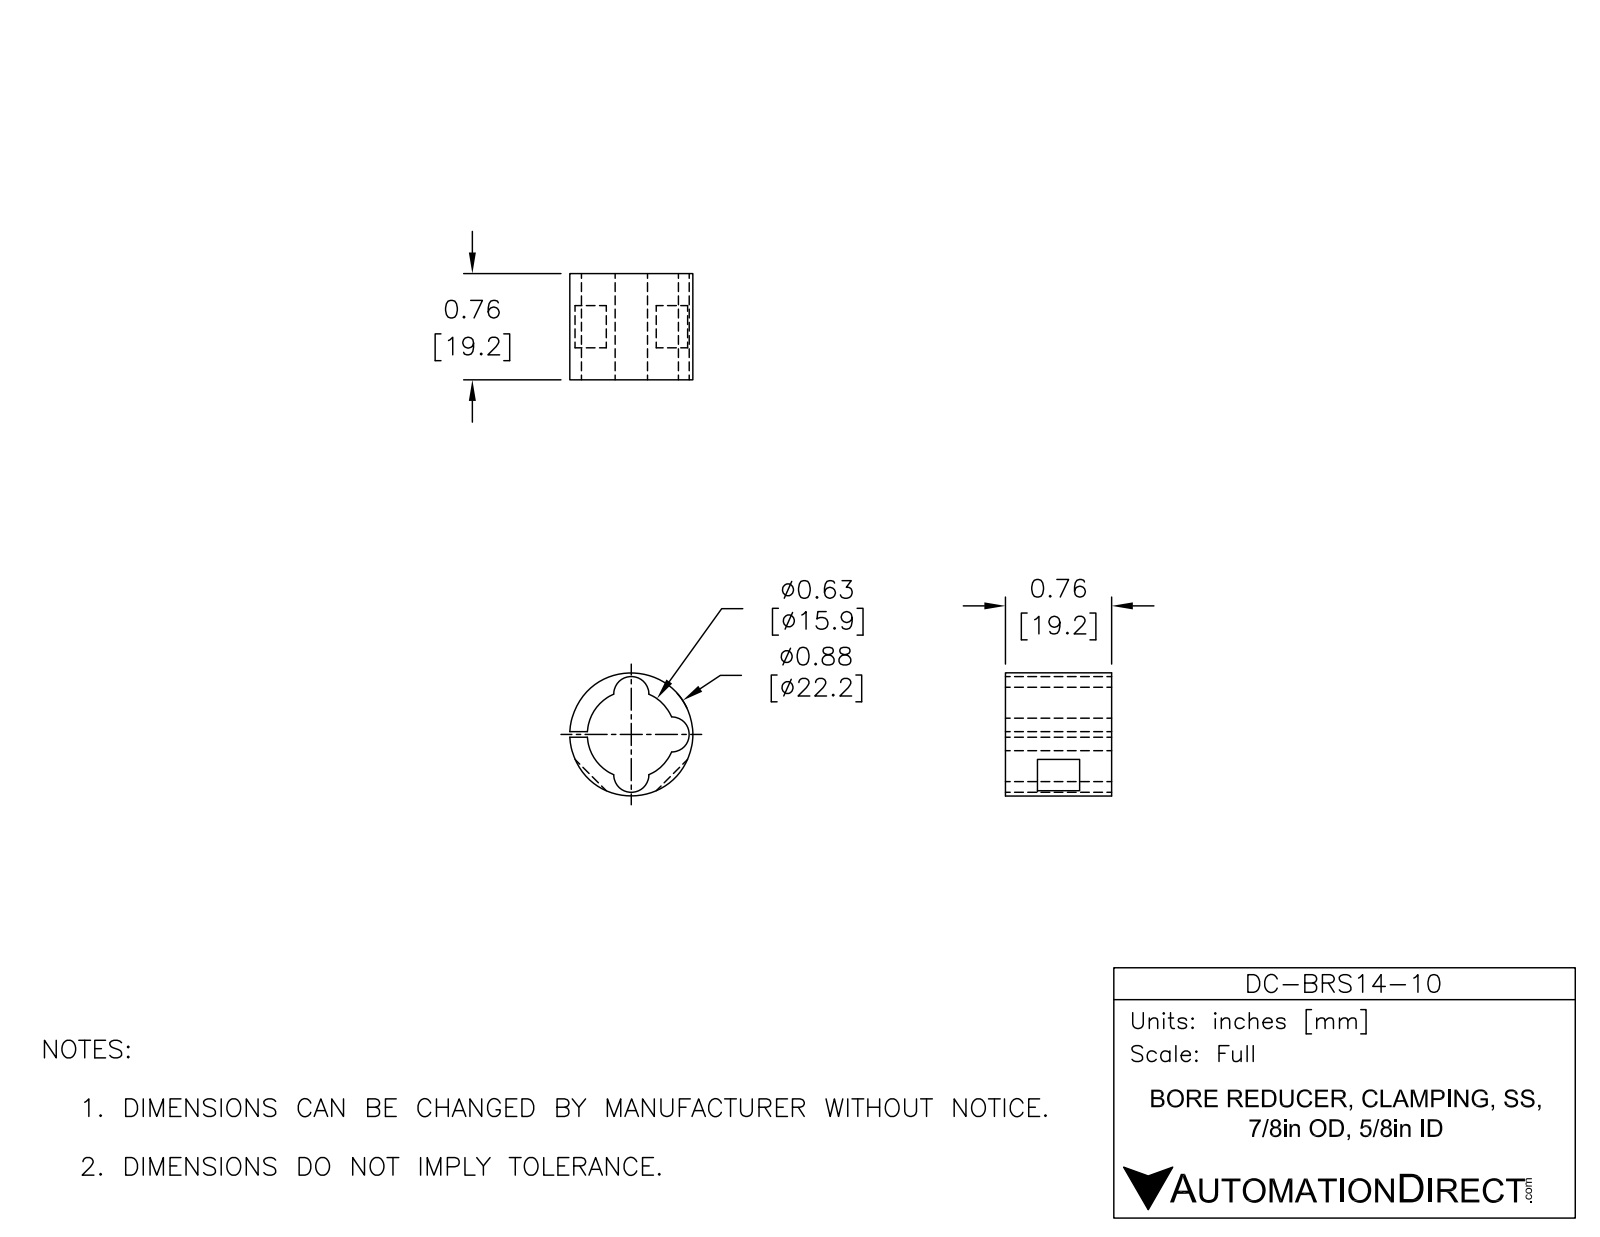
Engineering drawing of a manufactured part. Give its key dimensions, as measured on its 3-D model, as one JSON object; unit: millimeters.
{"part_name": "DC-BRS14-10", "step_written_by": "SolidWorks 2015 (AUTOMOTIVE_DESIGN)", "units": "millimeters", "bodies": {"solids": 1, "faces": 21, "planar": 10, "cylindrical": 11, "other": 0}, "overall_size": [22.23, 22.21, 19.18], "volume_mm3": 2774, "surface_area_mm2": 2885, "round_bosses_or_shafts": [[22.22, 1]], "partial_cylinders_radius": [[3.17, 3], [7.94, 1]], "face_to_face_distances": [19.18, 1.02, 5.78, 13.4, 7.62]}
